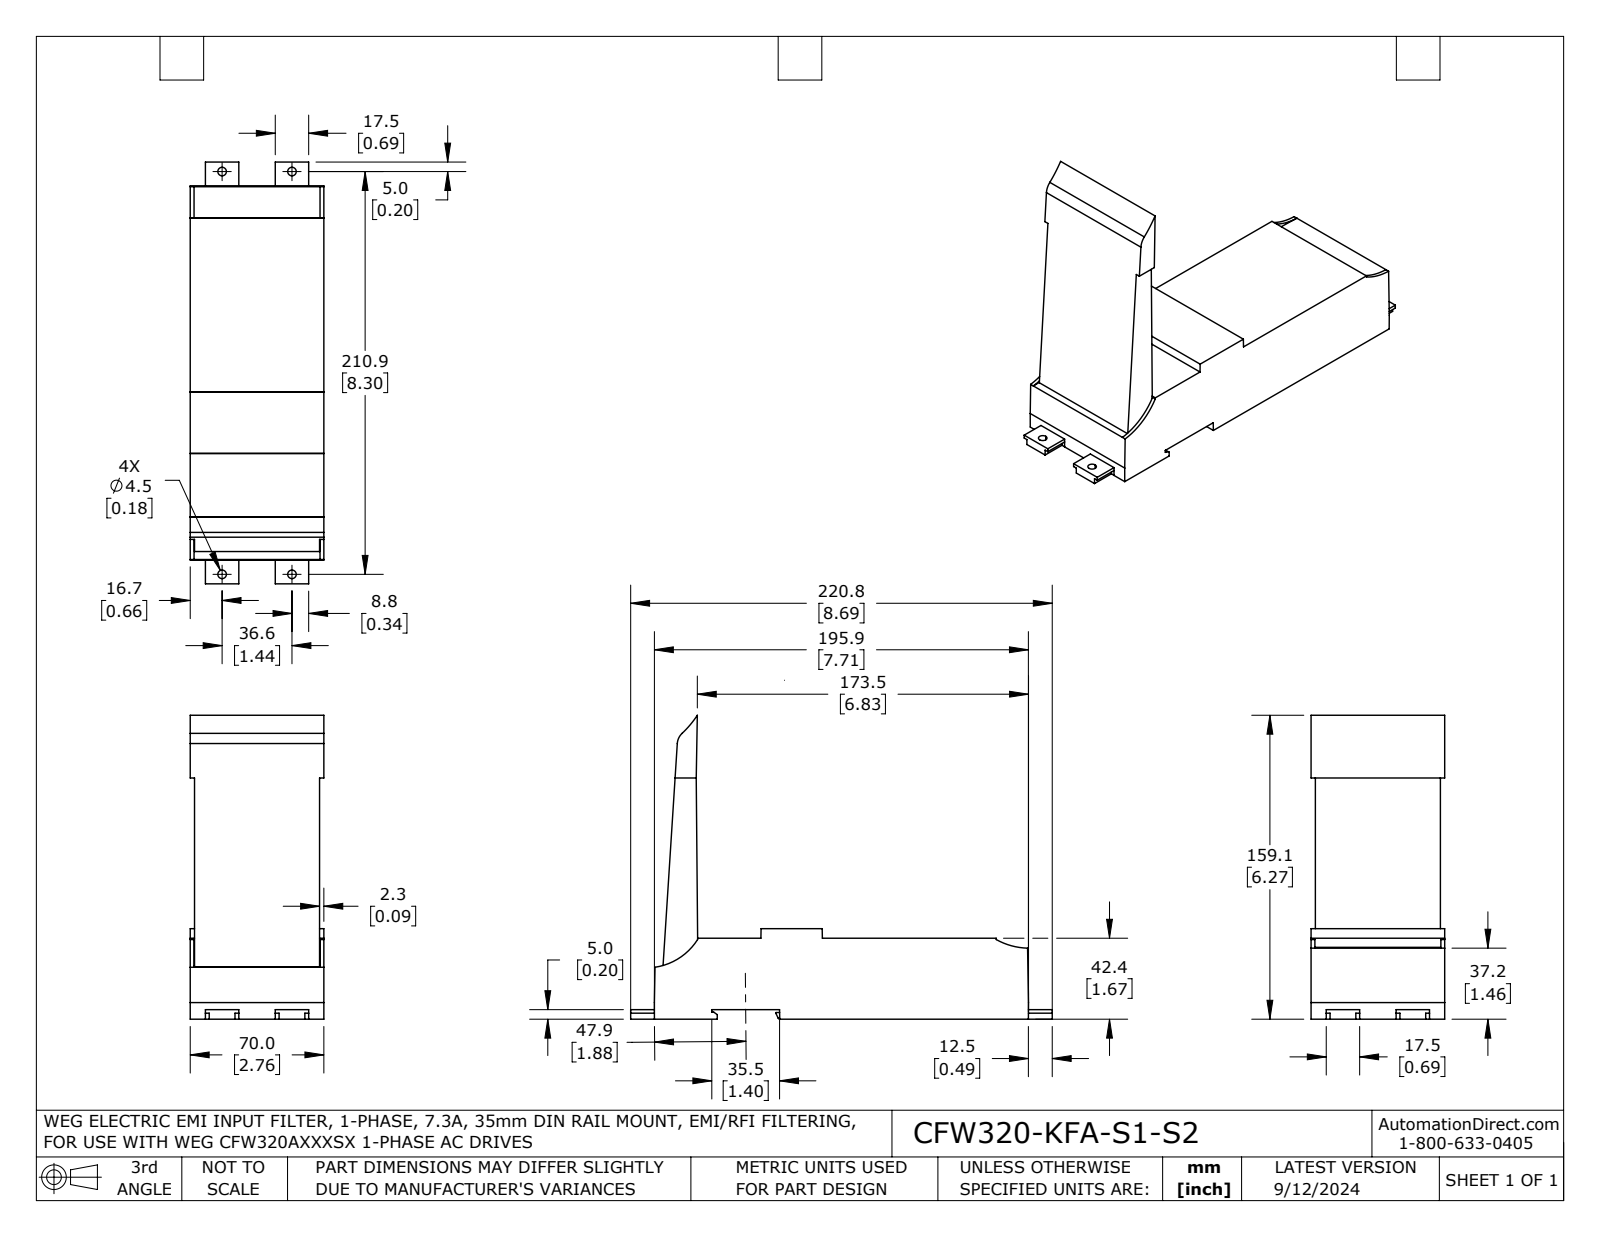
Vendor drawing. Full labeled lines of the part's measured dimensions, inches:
Part name (STEP PRODUCT): CFW320-KFA-S1-S2
STEP written by: SolidWorks 2021 (AUTOMOTIVE_DESIGN)
Units: inches
Bodies: 1 solid, 110 faces (95 planar, 15 cylindrical, 0 other)
Overall size (bounding box): 8.695 × 6.266 × 2.756
Volume: 40.8 in³ · Surface area: 110.9 in²
Round holes (diameter × count): ⌀0.177 ×4
Partial cylindrical surfaces — rounded edges, fillets, slot ends (radius × count): R0.039 ×1, R0.315 ×1, R1.26 ×1, R1.401 ×1, R2.081 ×1
Main face-to-face distances: 1.669, 2.756, 0.197, 1.472, 0.089, 2.667, 1.866, 2.579, 0.785, 0.079
Hole centre spacings: 1.441, 8.303, 8.427
